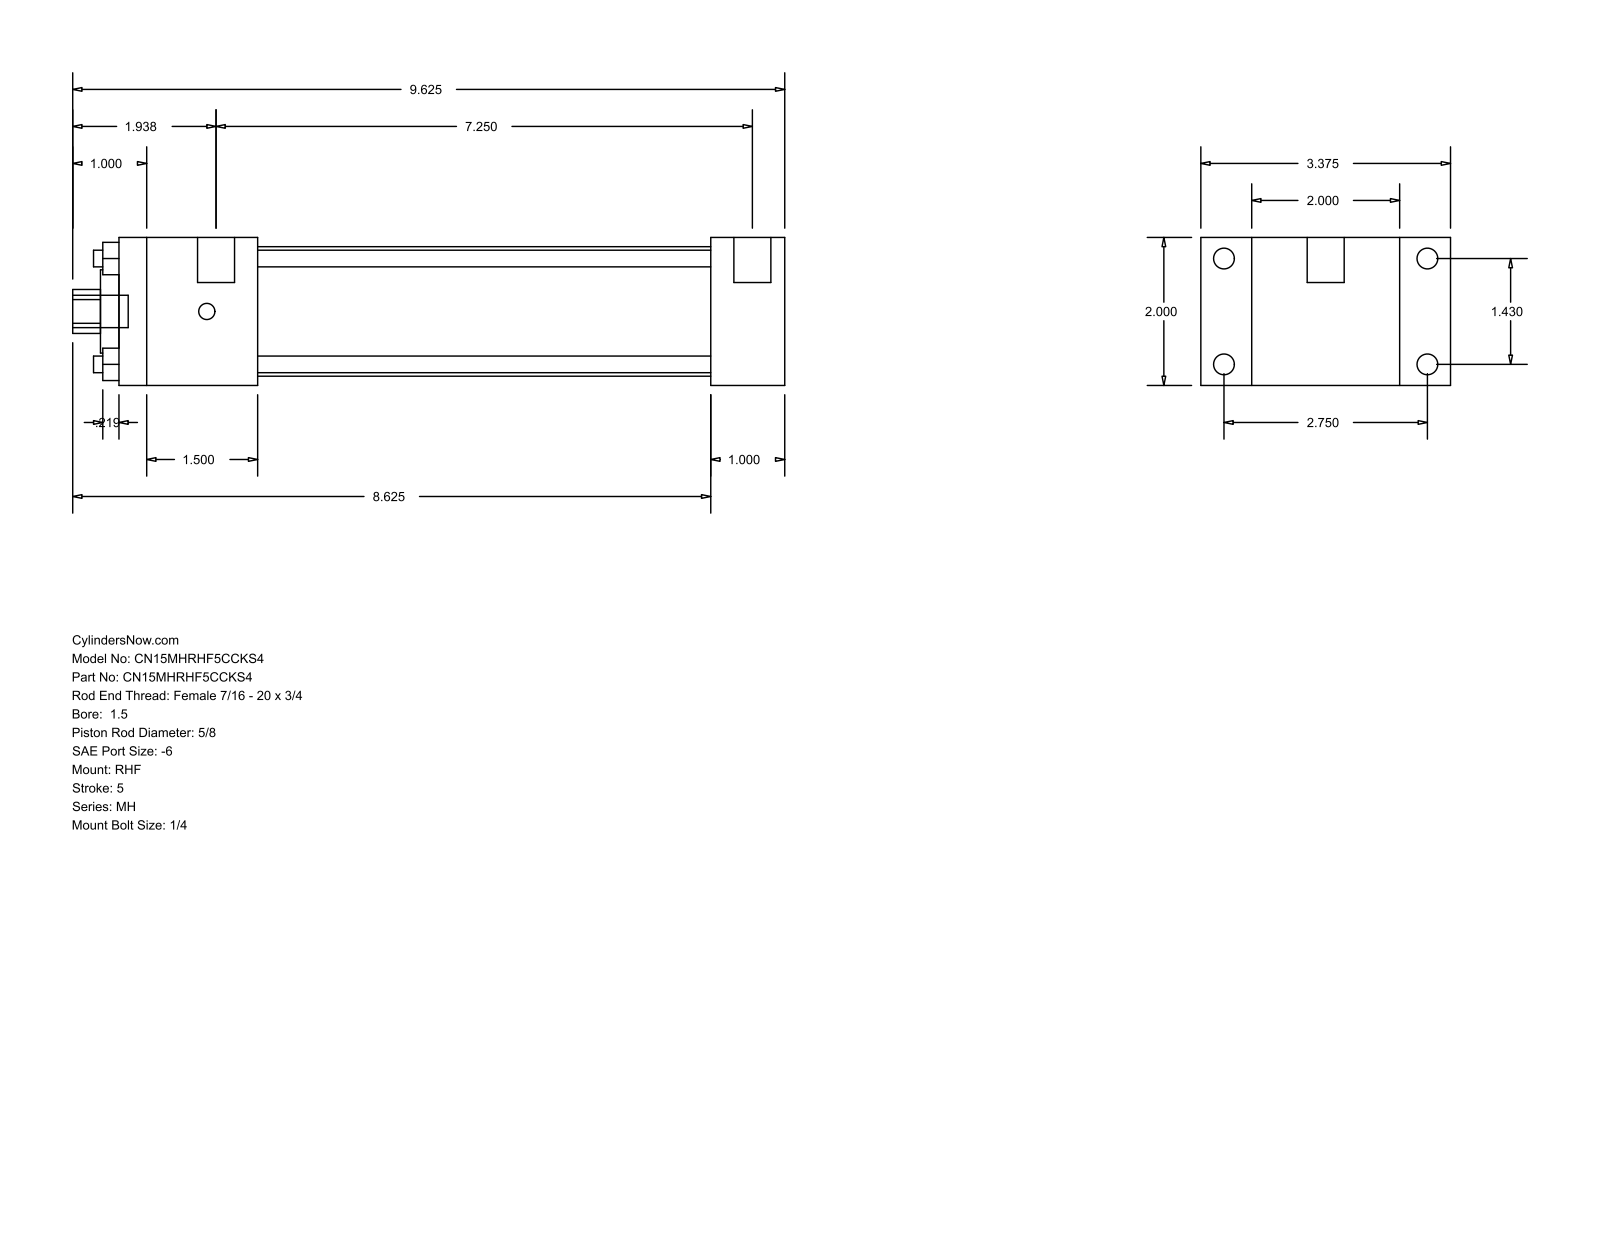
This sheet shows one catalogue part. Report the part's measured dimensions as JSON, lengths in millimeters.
{"part_name": "MH_RHF__0150_0.625", "step_written_by": "GSSL Pune (CONFIG_CONTROL_DESIGN)", "units": "millimeters", "bodies": {"solids": 0, "faces": 88, "planar": 60, "cylindrical": 28, "other": 0}, "overall_size": [244.47, 85.72, 50.8], "round_holes": [[5.71, 4], [15.88, 1], [28.57, 1], [44.45, 1]], "round_bosses_or_shafts": [[7.14, 4], [5.56, 4], [12.7, 2], [11.11, 1]], "partial_cylinders_radius": [[7.54, 1]], "face_to_face_distances": [50.8, 17.46, 68.26, 25.4, 203.19, 228.59, 85.72, 47.62, 155.57, 180.97], "hole_center_spacings": [25.68, 36.32, 51.36]}
